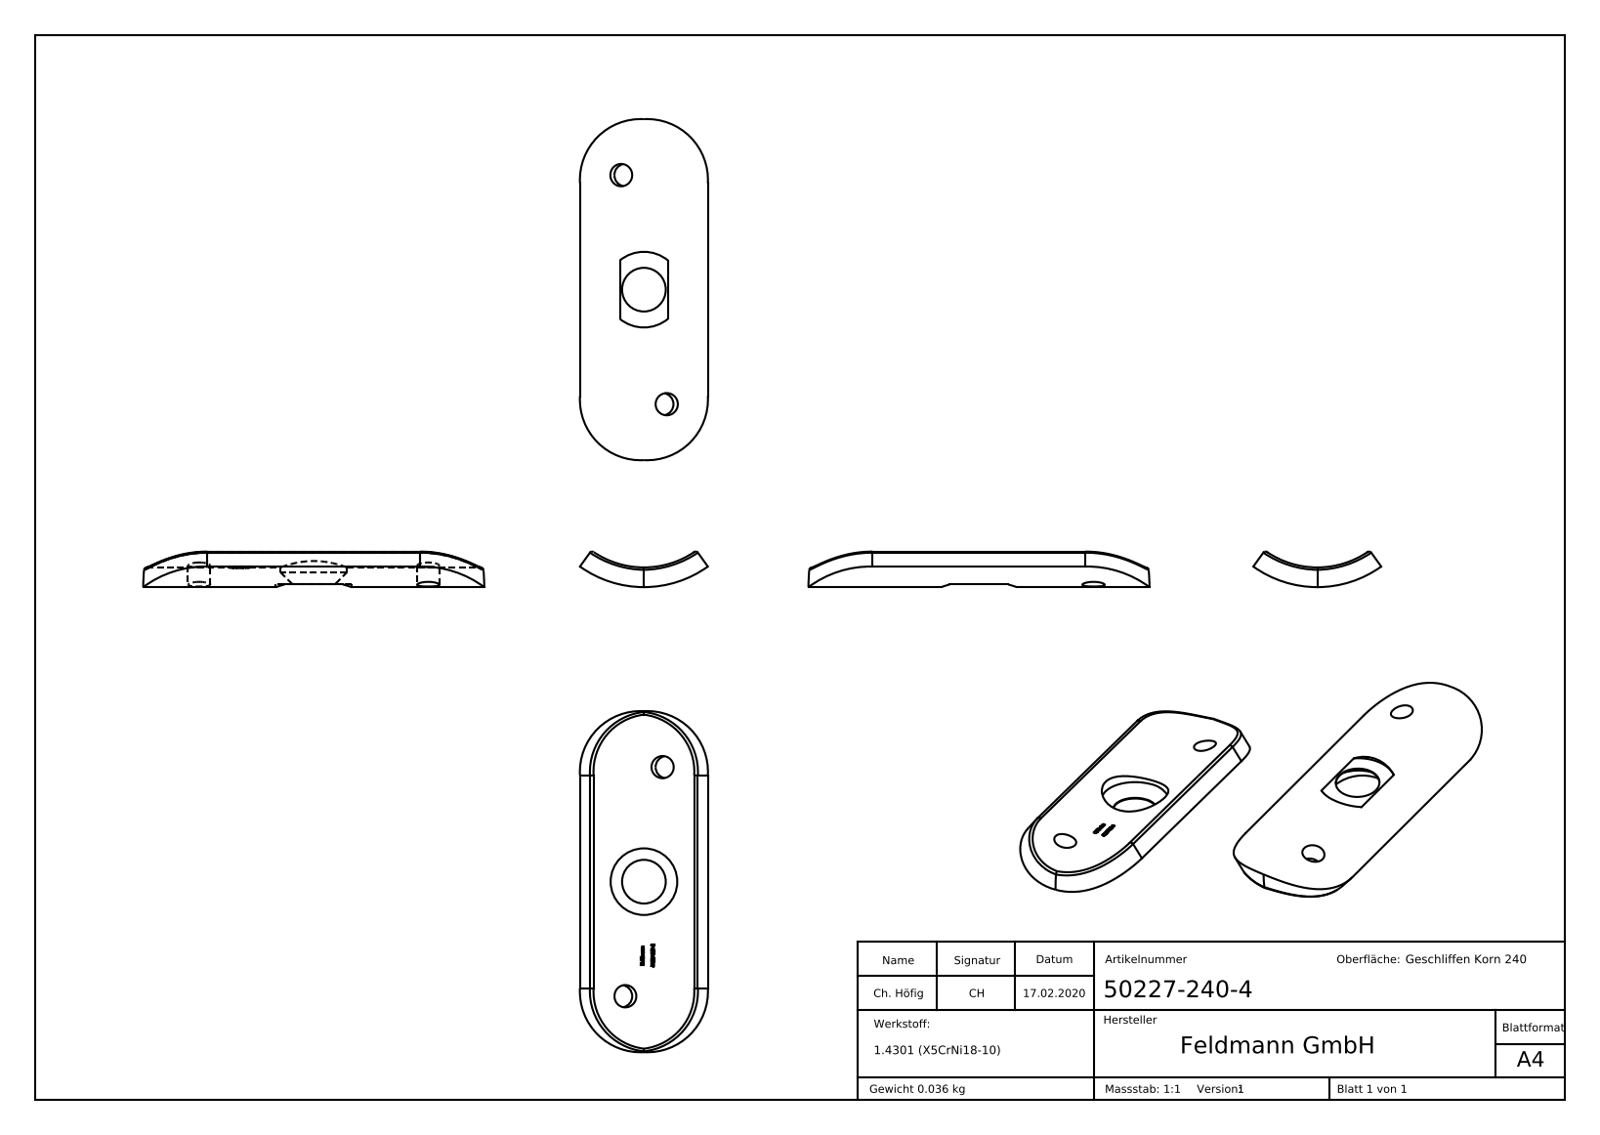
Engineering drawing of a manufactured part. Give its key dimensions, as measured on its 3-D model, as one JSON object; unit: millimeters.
{"part_name": "50227-240-4", "step_written_by": "SolidWorks 2018 (CONFIG_CONTROL_DESIGN)", "units": "millimeters", "bodies": {"solids": 1, "faces": 264, "planar": 121, "cylindrical": 45, "other": 98}, "overall_size": [64, 24, 6.68], "volume_mm3": 4568, "surface_area_mm2": 3312, "round_holes": [[4.2, 2], [8.2, 1], [12.5, 1]], "partial_cylinders_radius": [[12, 4], [0.5, 2], [7.1, 1], [16.85, 1], [16.95, 1], [20.55, 1]], "face_to_face_distances": [0.55, 0.5, 1.74, 1.9, 1.79, 0.53, 1.06, 1.84, 0.6, 1.78]}
